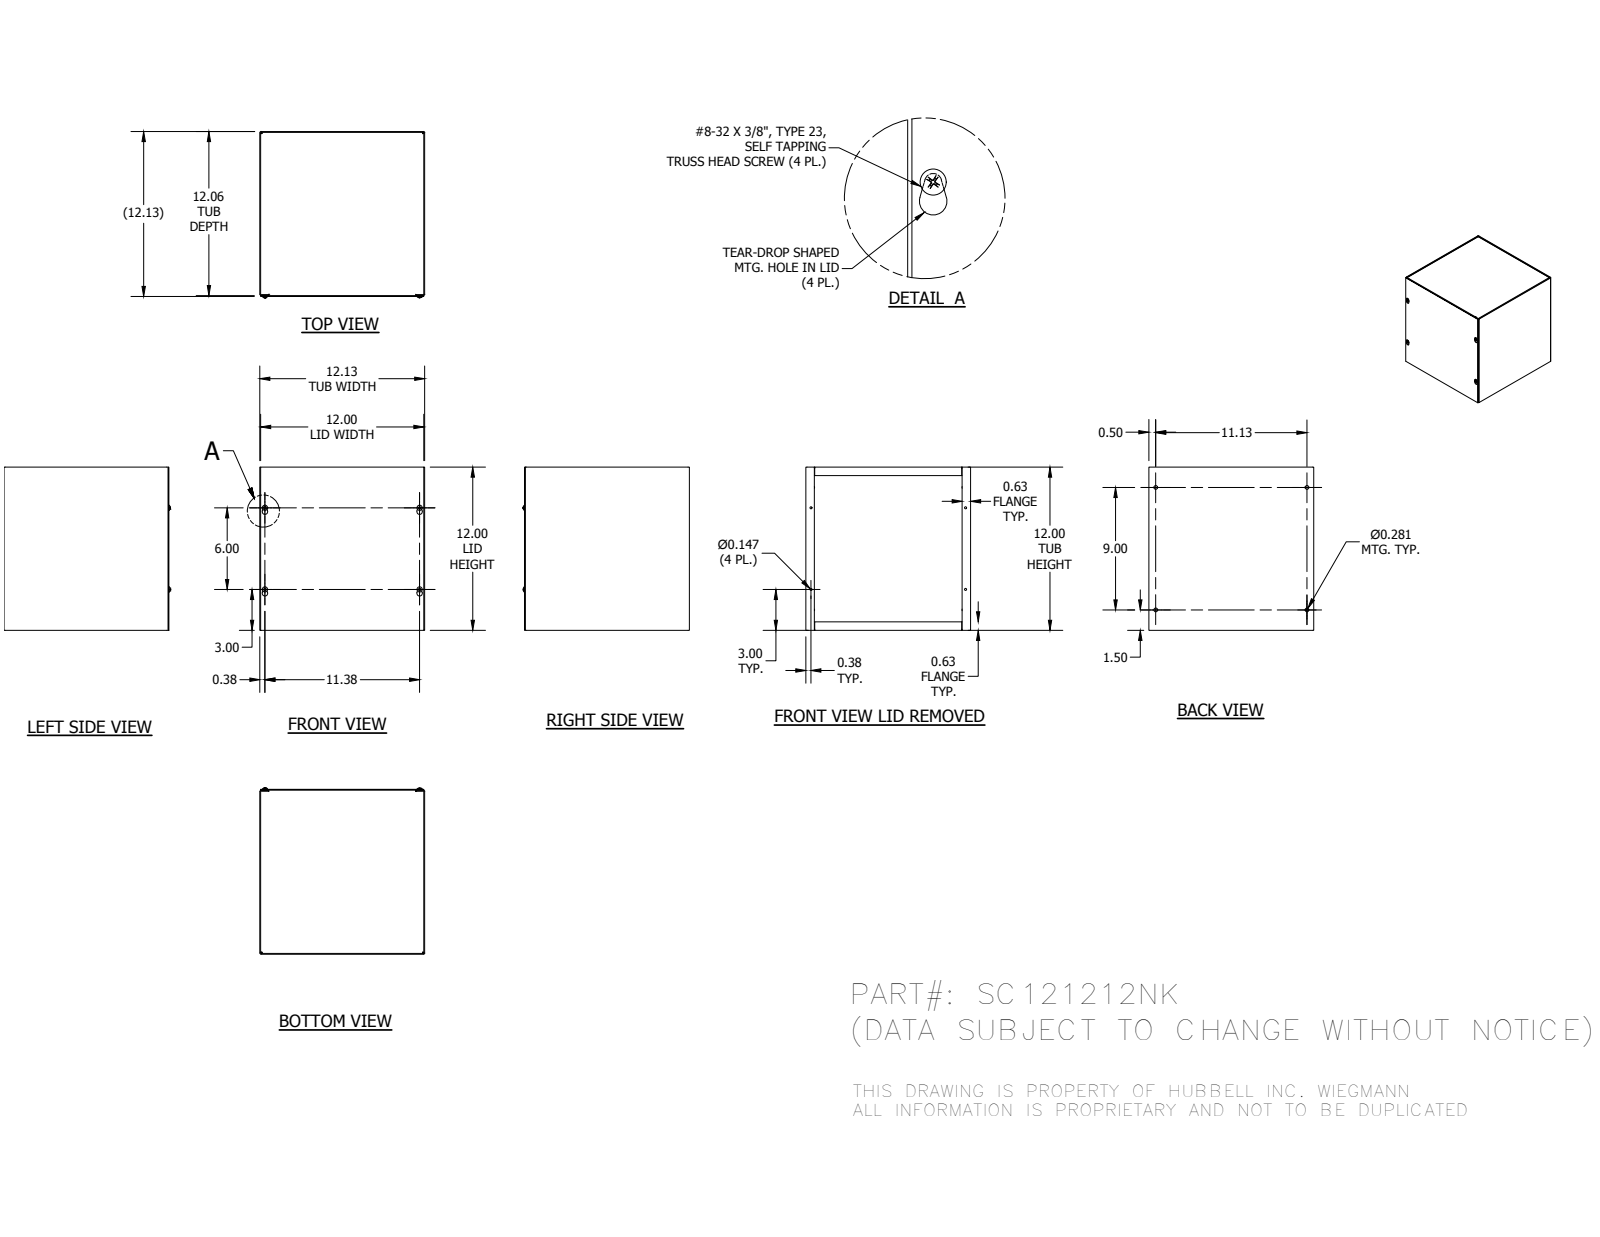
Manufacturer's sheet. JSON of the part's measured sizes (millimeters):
{"part_name": "SC121212NKBLR; SC1212NKTB; SC1212LPA; 34056 (+1 more)", "step_written_by": "Autodesk Inventor 2014 (AUTOMOTIVE_DESIGN)", "units": "millimeters", "bodies": {"solids": 8, "faces": 268, "planar": 152, "cylindrical": 48, "other": 68}, "overall_size": [310.52, 307.98, 304.8], "volume_mm3": 949439, "surface_area_mm2": 1207000, "round_holes": [[3.73, 4], [7.14, 4]], "round_bosses_or_shafts": [[9.75, 4], [4.17, 4]], "partial_cylinders_radius": [[0.79, 12], [2.38, 12], [3.17, 4], [5.16, 4]], "face_to_face_distances": [1.59, 304.8, 306.39, 303.21, 1.58, 301.62, 306.38, 307.97, 307.98, 3.17], "hole_center_spacings": [38.23, 190.53, 288.28, 343.43, 152.4, 228.6, 282.58, 288.92]}
